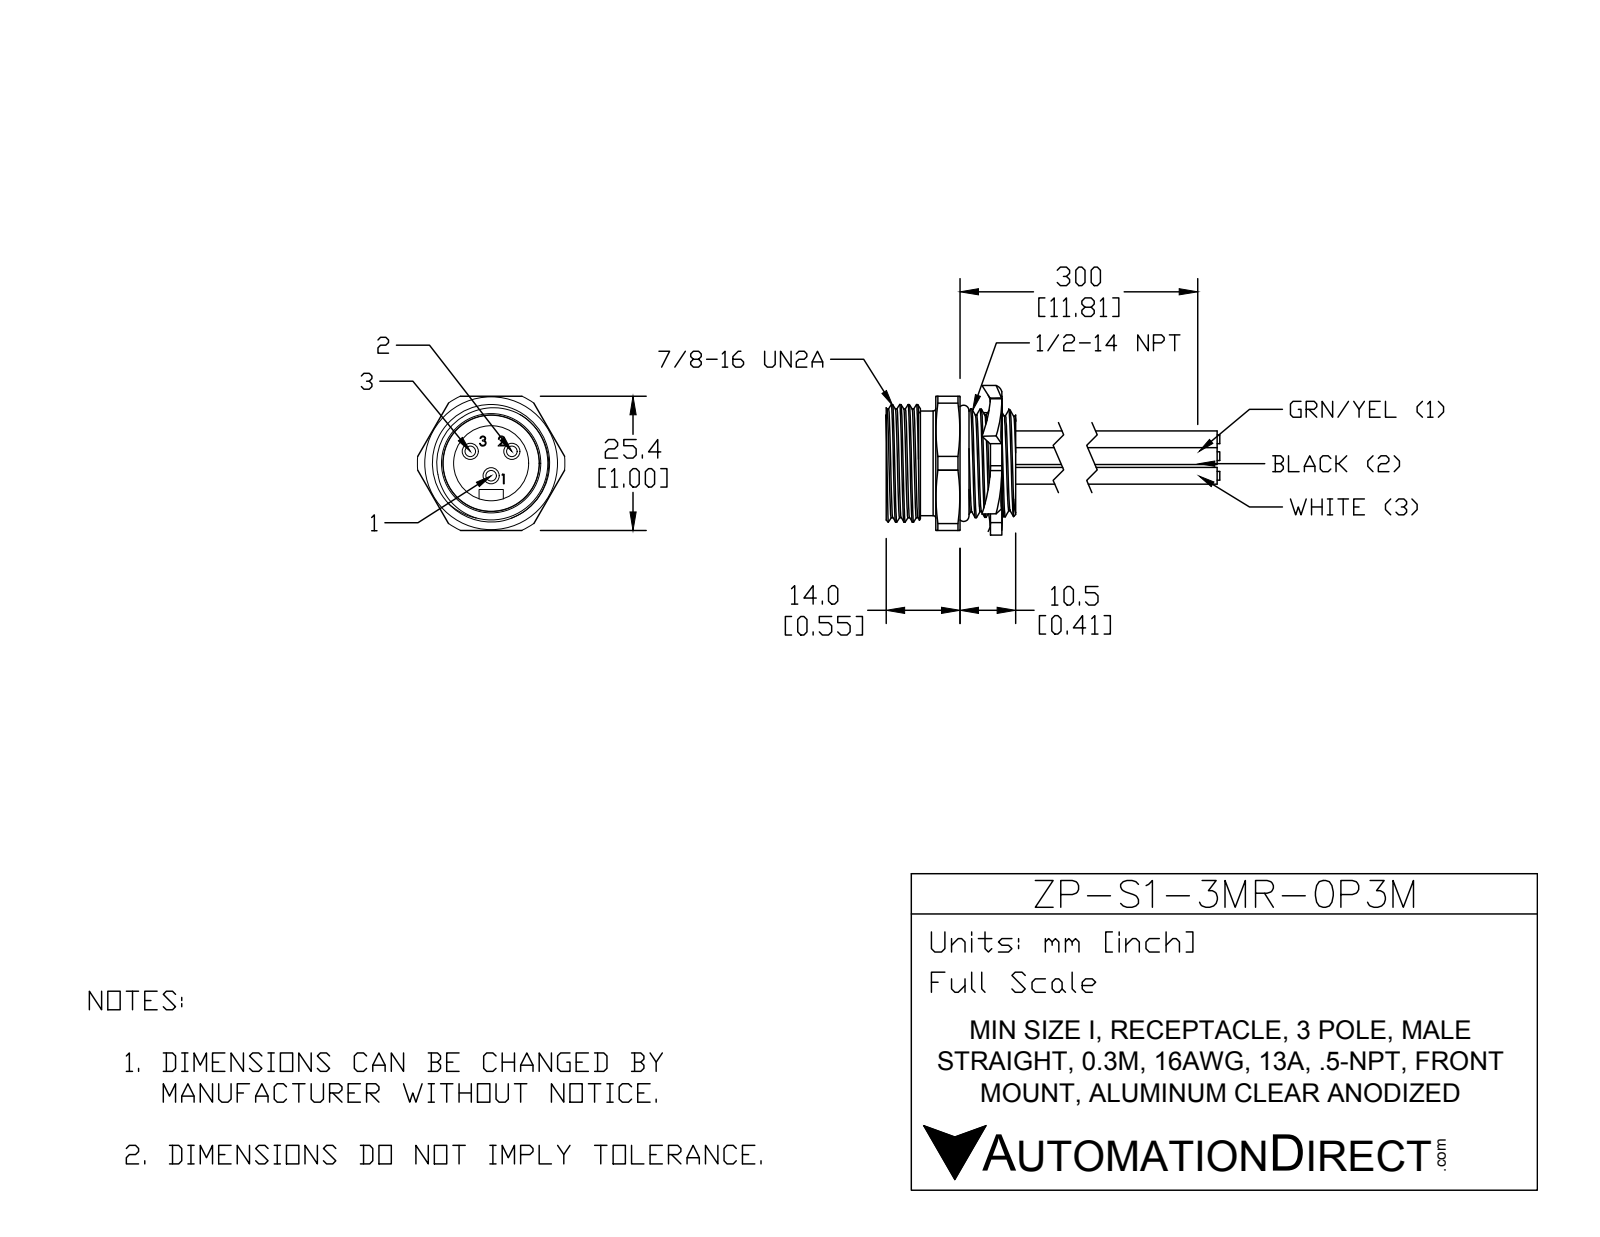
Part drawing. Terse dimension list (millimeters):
name: MIN-3MR-ZZ
written by: SolidWorks 2015 (AUTOMOTIVE_DESIGN)
unit: mm
bodies: 1 solid, 219 faces (65 planar, 68 cylindrical, 86 other)
size: 49.91 × 29.77 × 29.48
volume: 8 867 mm³; area: 6 330 mm²
holes: 1× ⌀14.22, 1× ⌀18.29, 1× ⌀19.61
bosses: 3× ⌀3.18, 3× ⌀3.05, 3× ⌀2, 1× ⌀25.37, 1× ⌀22.22, 1× ⌀20.6, 1× ⌀19.81, 1× ⌀18.14
rounds: 1× R2.29, 1× R13.97
face distances: 25.4, 6.35, 12.37, 15.11, 4.57, 10.54, 6.02, 1.45, 16.56, 7.8
